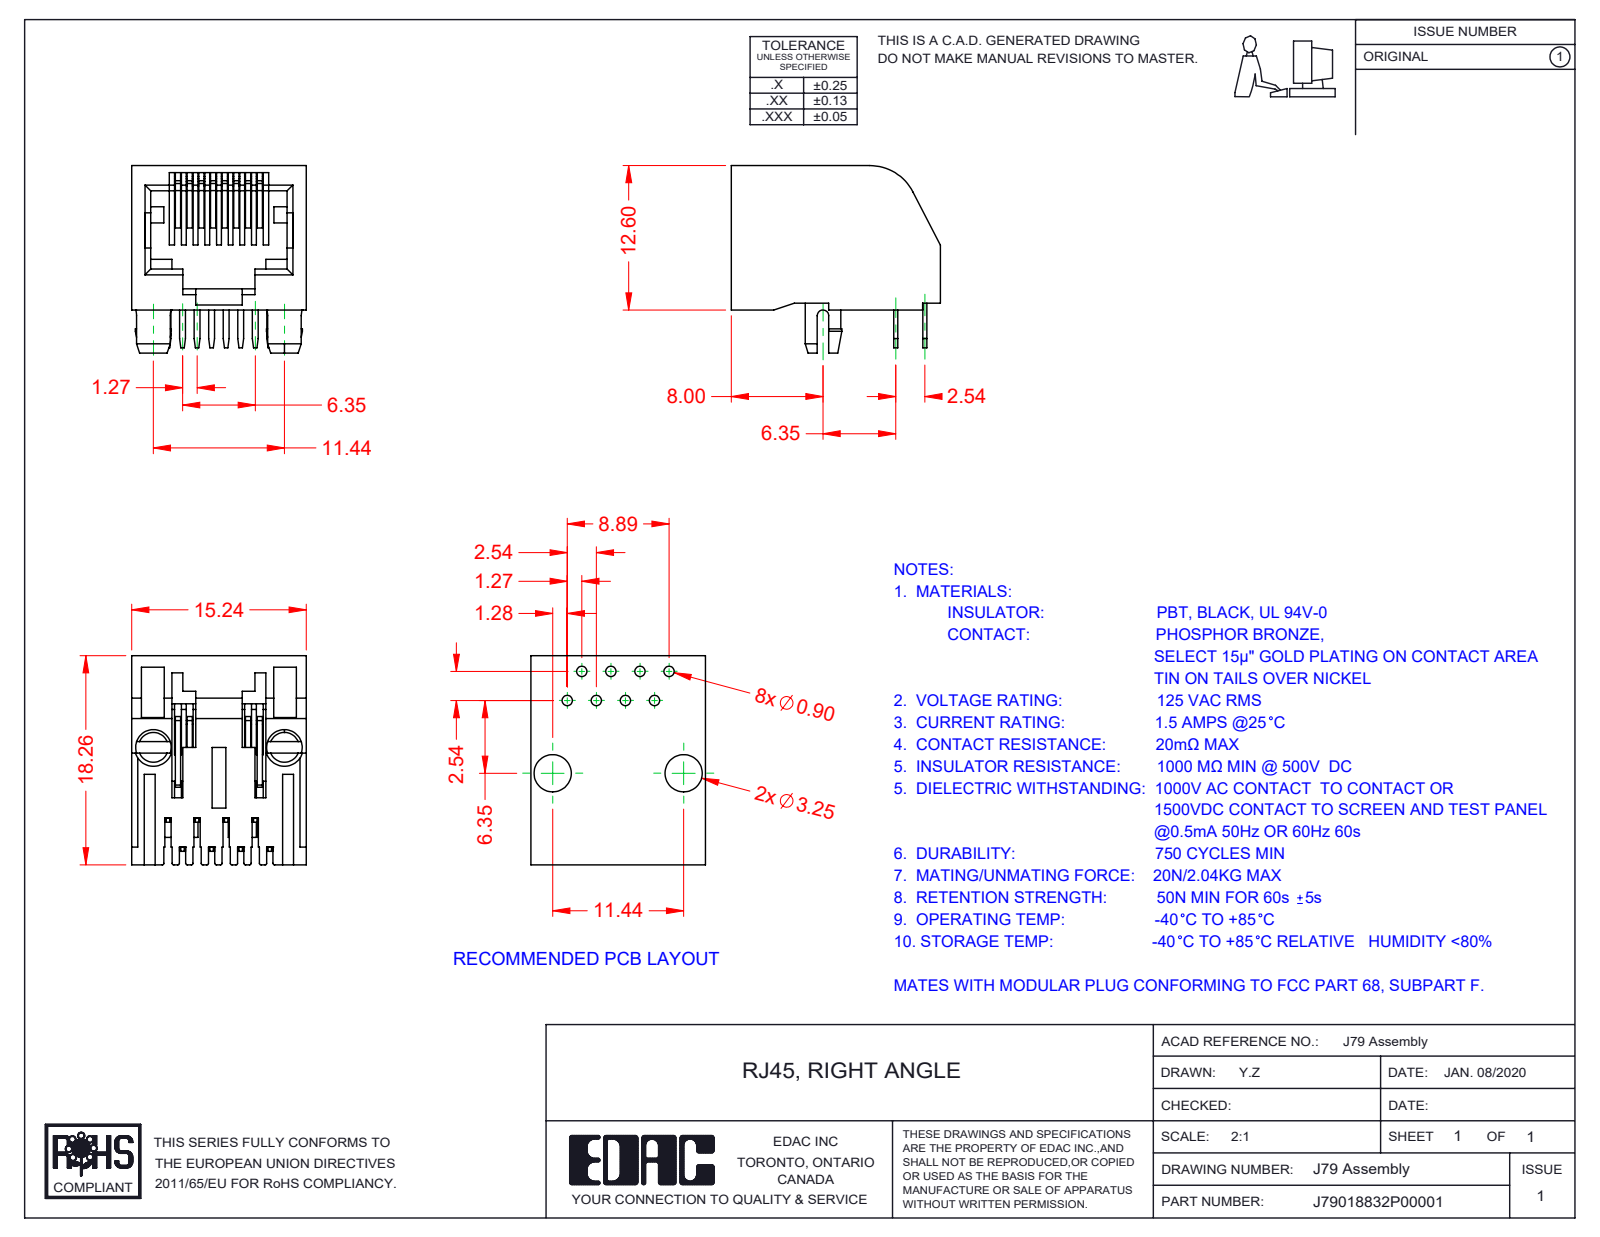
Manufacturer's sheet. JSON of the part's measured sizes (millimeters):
{"part_name": "RJ79018832P00001; 79 Contacts; 79 Insulator", "step_written_by": "SolidWorks 2016 (CONFIG_CONTROL_DESIGN)", "units": "millimeters", "bodies": {"solids": 9, "faces": 574, "planar": 424, "cylindrical": 144, "other": 6}, "overall_size": [18.26, 16.36, 15.24], "volume_mm3": 1496, "surface_area_mm2": 3263, "round_bosses_or_shafts": [[3.1, 2]], "partial_cylinders_radius": [[0.15, 16], [0.5, 7], [0.72, 3], [0.36, 2], [1.65, 2], [1.8, 2], [2.16, 2], [0.2, 1]], "face_to_face_distances": [15.24, 2.04, 0.6, 12, 0.36, 4.08, 1.25, 9.8, 2.2, 8.2]}
